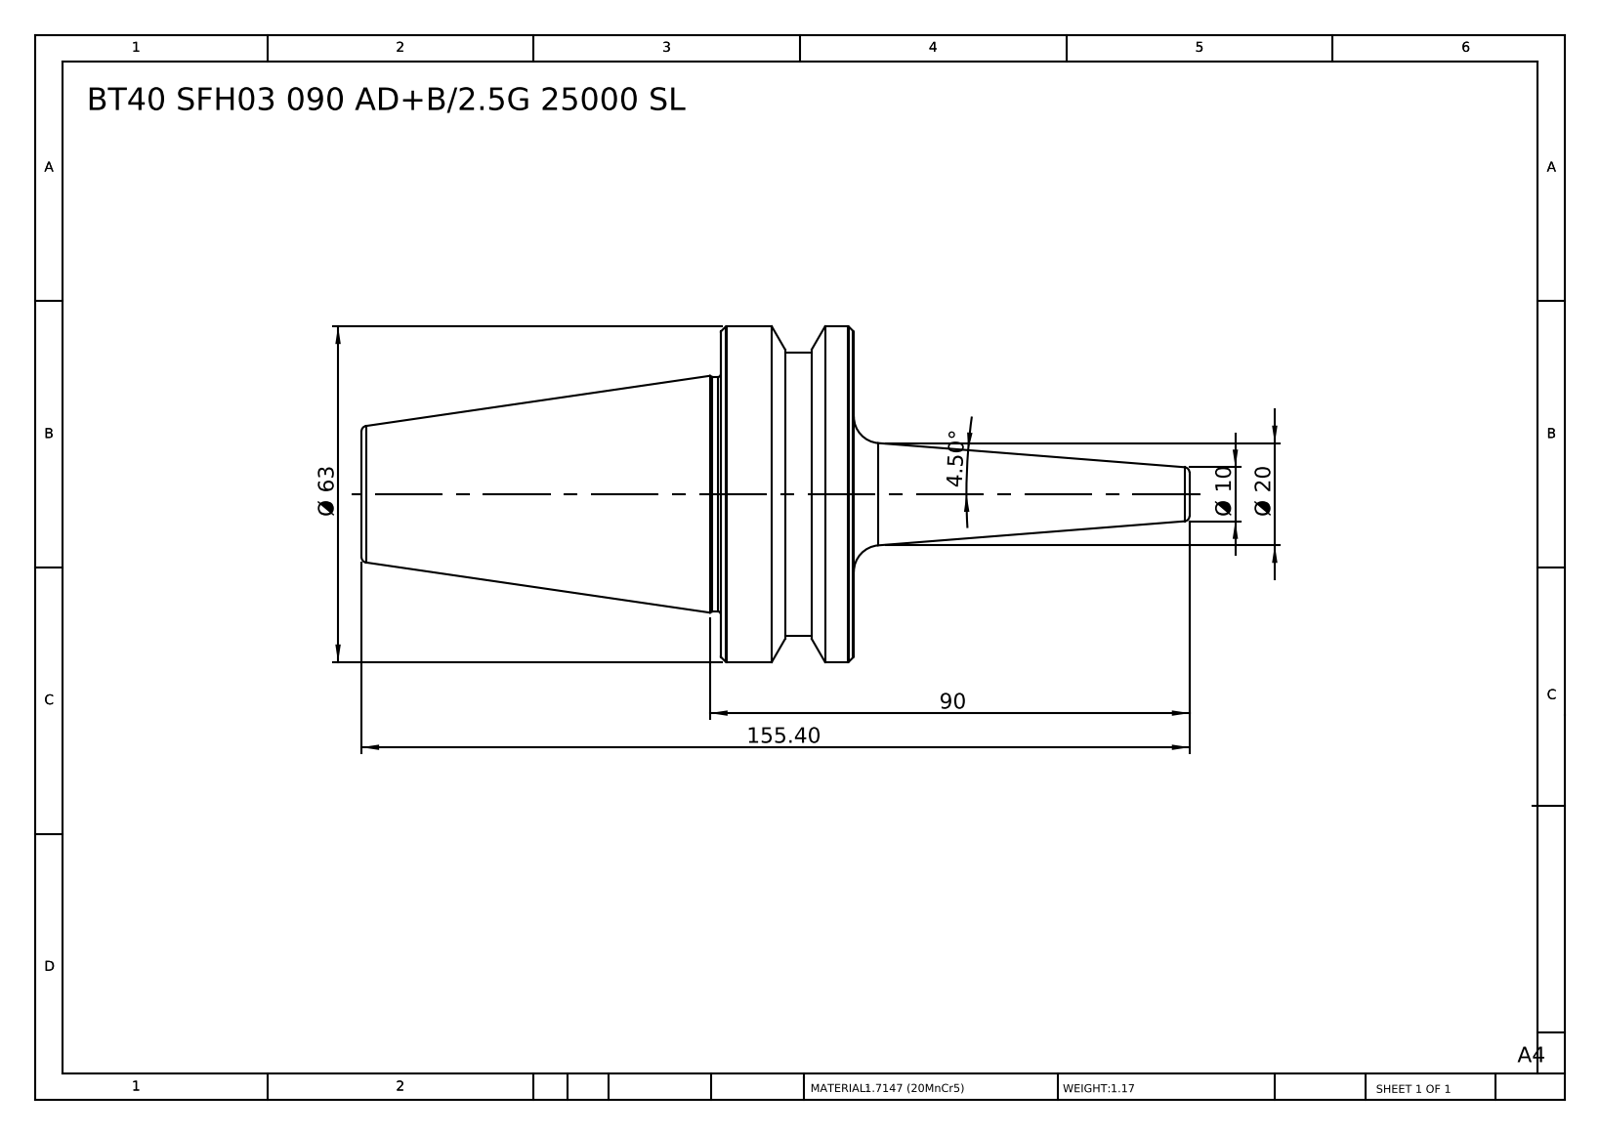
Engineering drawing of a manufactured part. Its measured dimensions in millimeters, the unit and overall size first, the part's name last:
Units: millimetres
Overall size (bounding box): 155.4 × 63 × 63
Round bosses / shafts (diameter × count): ⌀63 ×1, ⌀53 ×1, ⌀44 ×1
Main face-to-face distances: 25, 92.4, 67.4, 7.9, 17.1, 84.5, 12.9, 5, 12.1, 79.5
Volume: 150 118 mm³ · Surface area: 20 944 mm²
Bodies: 1 solid, 44 faces (6 planar, 8 cylindrical, 30 other)
Part name (STEP PRODUCT): BT40 SFH03 090 AD+B-2.5G 25000 SL
STEP written by: SolidWorks 2014 (CONFIG_CONTROL_DESIGN)
